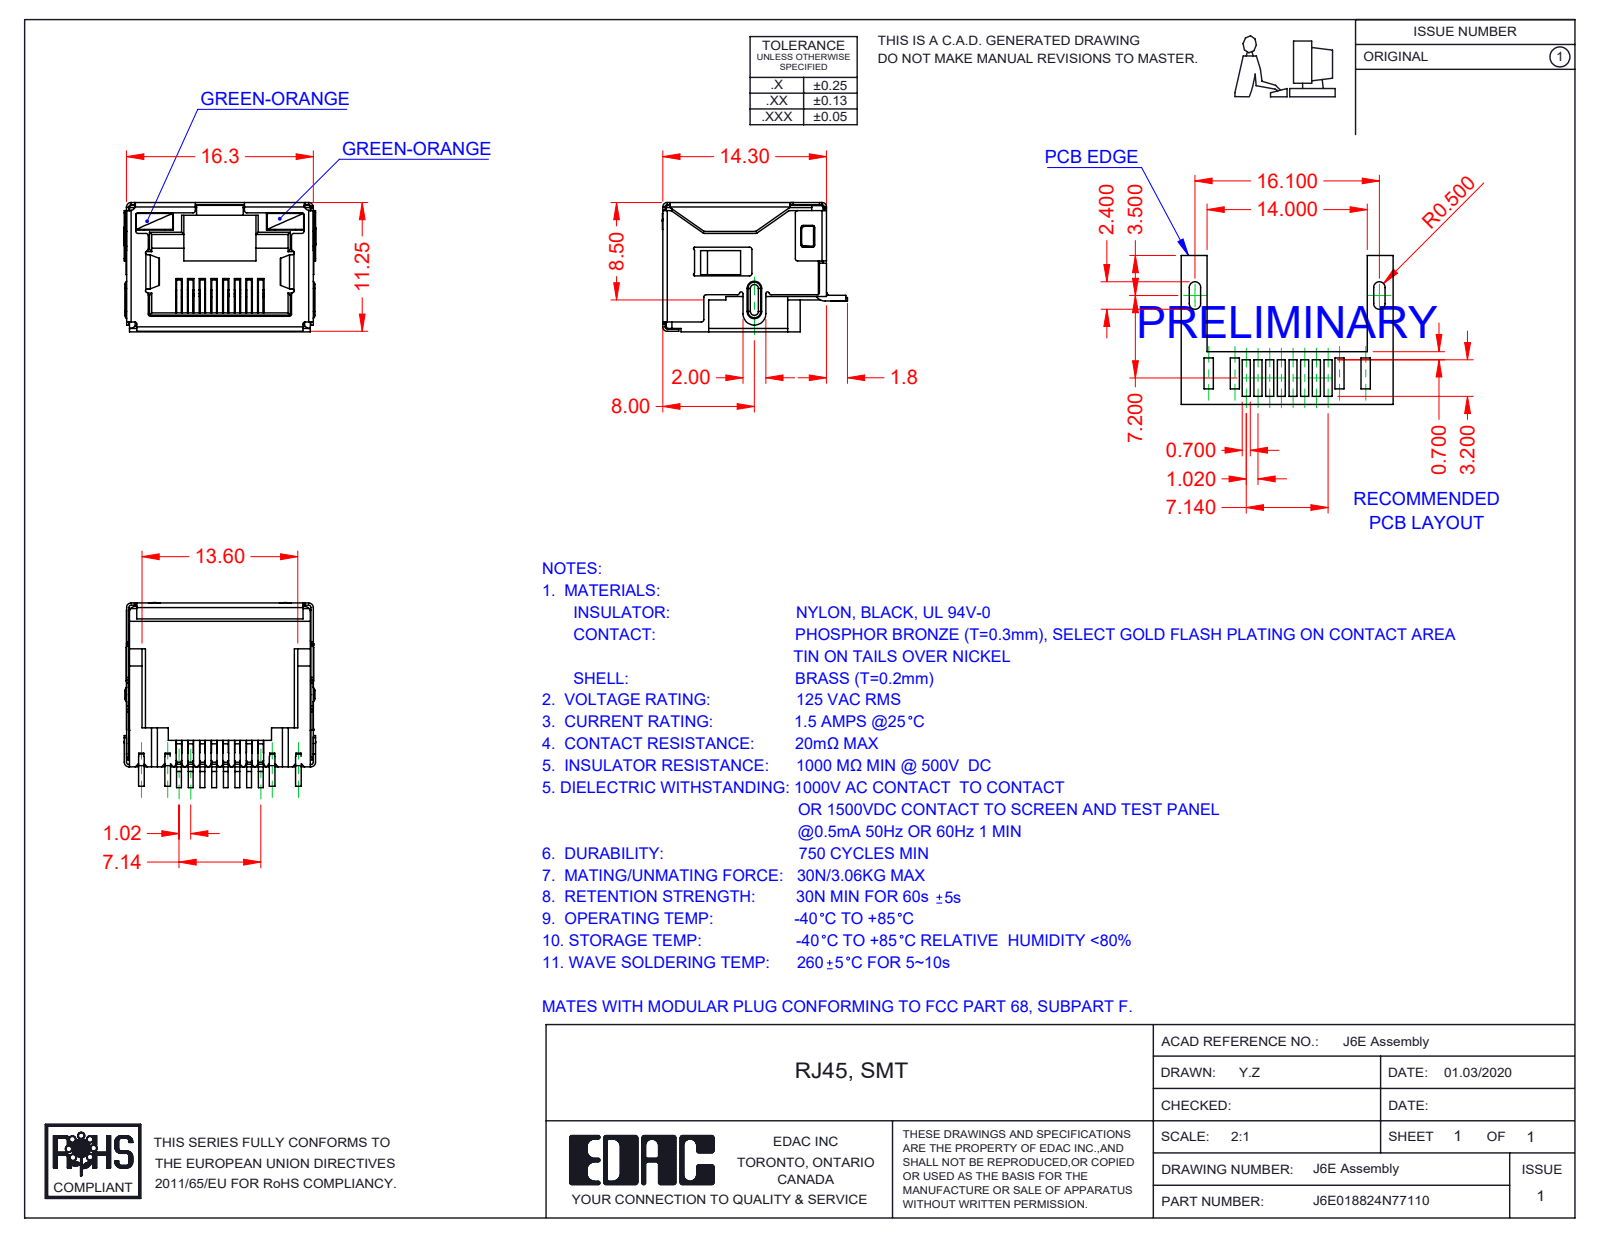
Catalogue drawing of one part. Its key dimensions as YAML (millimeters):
part_name: "6E LED LH_7-Green-Orange; J6E018824N77110; 6E Shield_LED; 6E Contacts (+2 more)"
step_written_by: "SolidWorks 2016 (CONFIG_CONTROL_DESIGN)"
units: millimeters
bodies: {solids: 12, faces: 1500, planar: 1099, cylindrical: 351, other: 50}
overall_size: [16.75, 16.15, 11.3]
volume: 1109
surface_area: 4045
partial_cylinders:
  - {radius: 0.2, count: 82}
  - {radius: 0.25, count: 17}
  - {radius: 0.4, count: 13}
  - {radius: 0.5, count: 13}
  - {radius: 0.1, count: 10}
  - {radius: 0.15, count: 7}
  - {radius: 0.3, count: 4}
  - {radius: 1, count: 3}
face_to_face_distances: [11.05, 16.05, 16.1, 15.85, 11.1, 11.3, 2.4, 0.7, 9.85, 0.49]
